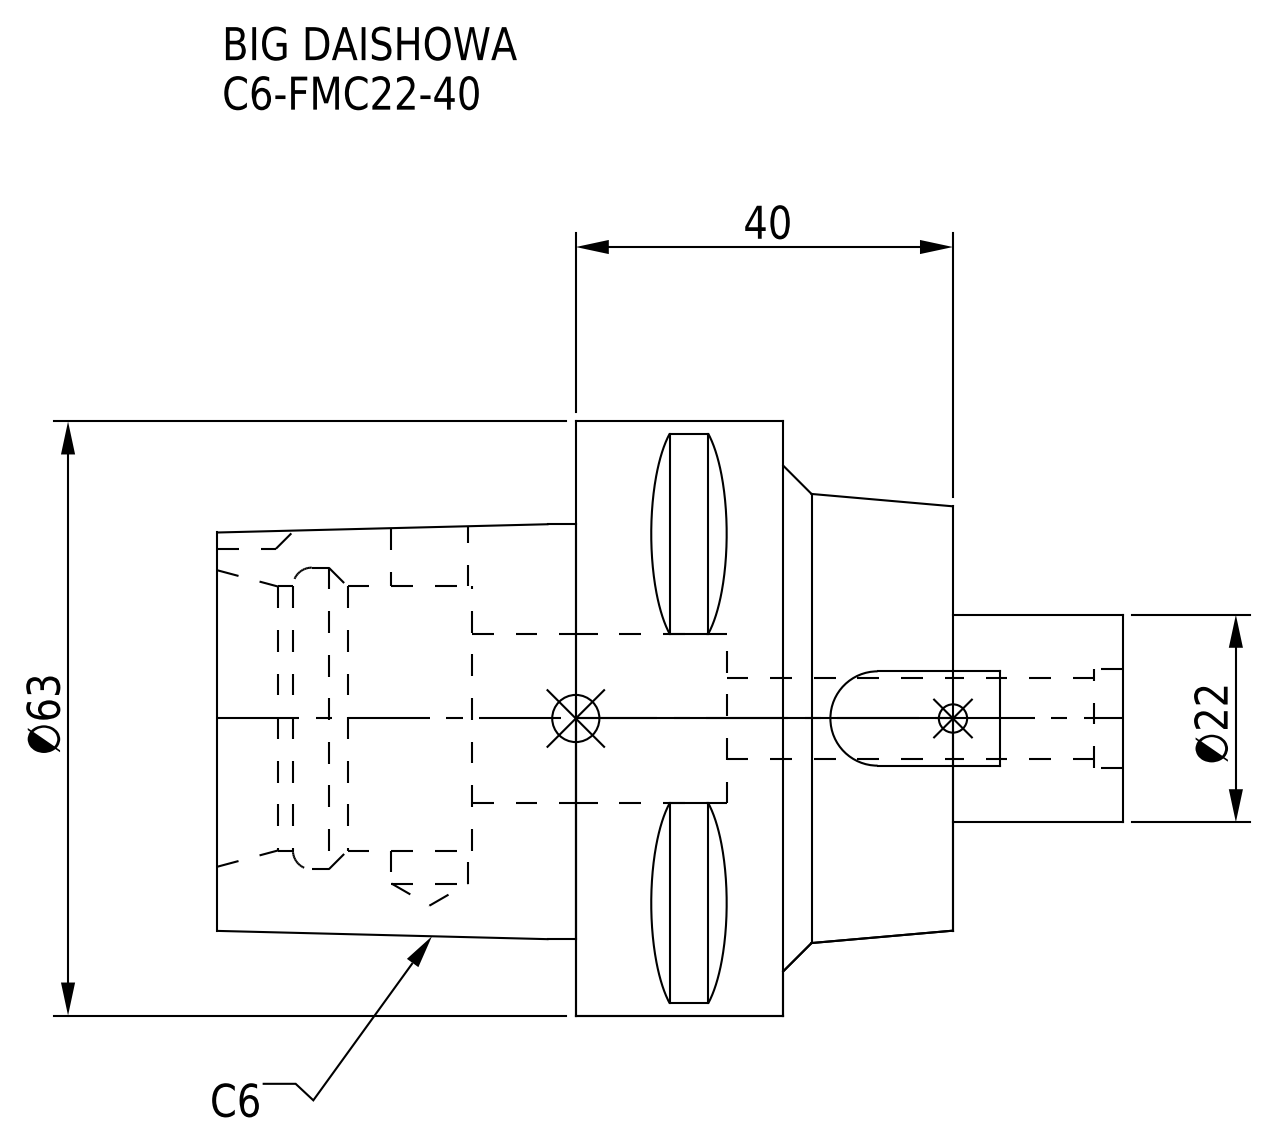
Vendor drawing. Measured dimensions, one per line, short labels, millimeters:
name: C6-FMC22-40
written by: CREO PARAMETRIC BY PTC INC, 2016380 (AUTOMOTIVE_DESIGN)
unit: mm
bodies: 1 solid, 81 faces (46 planar, 21 cylindrical, 14 other)
size: 96 × 63 × 63
volume: 133 273 mm³; area: 25 018 mm²
holes: 1× ⌀8.1, 1× ⌀8.5, 1× ⌀10.5, 1× ⌀18, 1× ⌀28, 1× ⌀32
bosses: 1× ⌀63, 1× ⌀22
rounds: 1× R5
face distances: 18, 40, 22, 27, 78, 60, 38, 33, 51, 11
